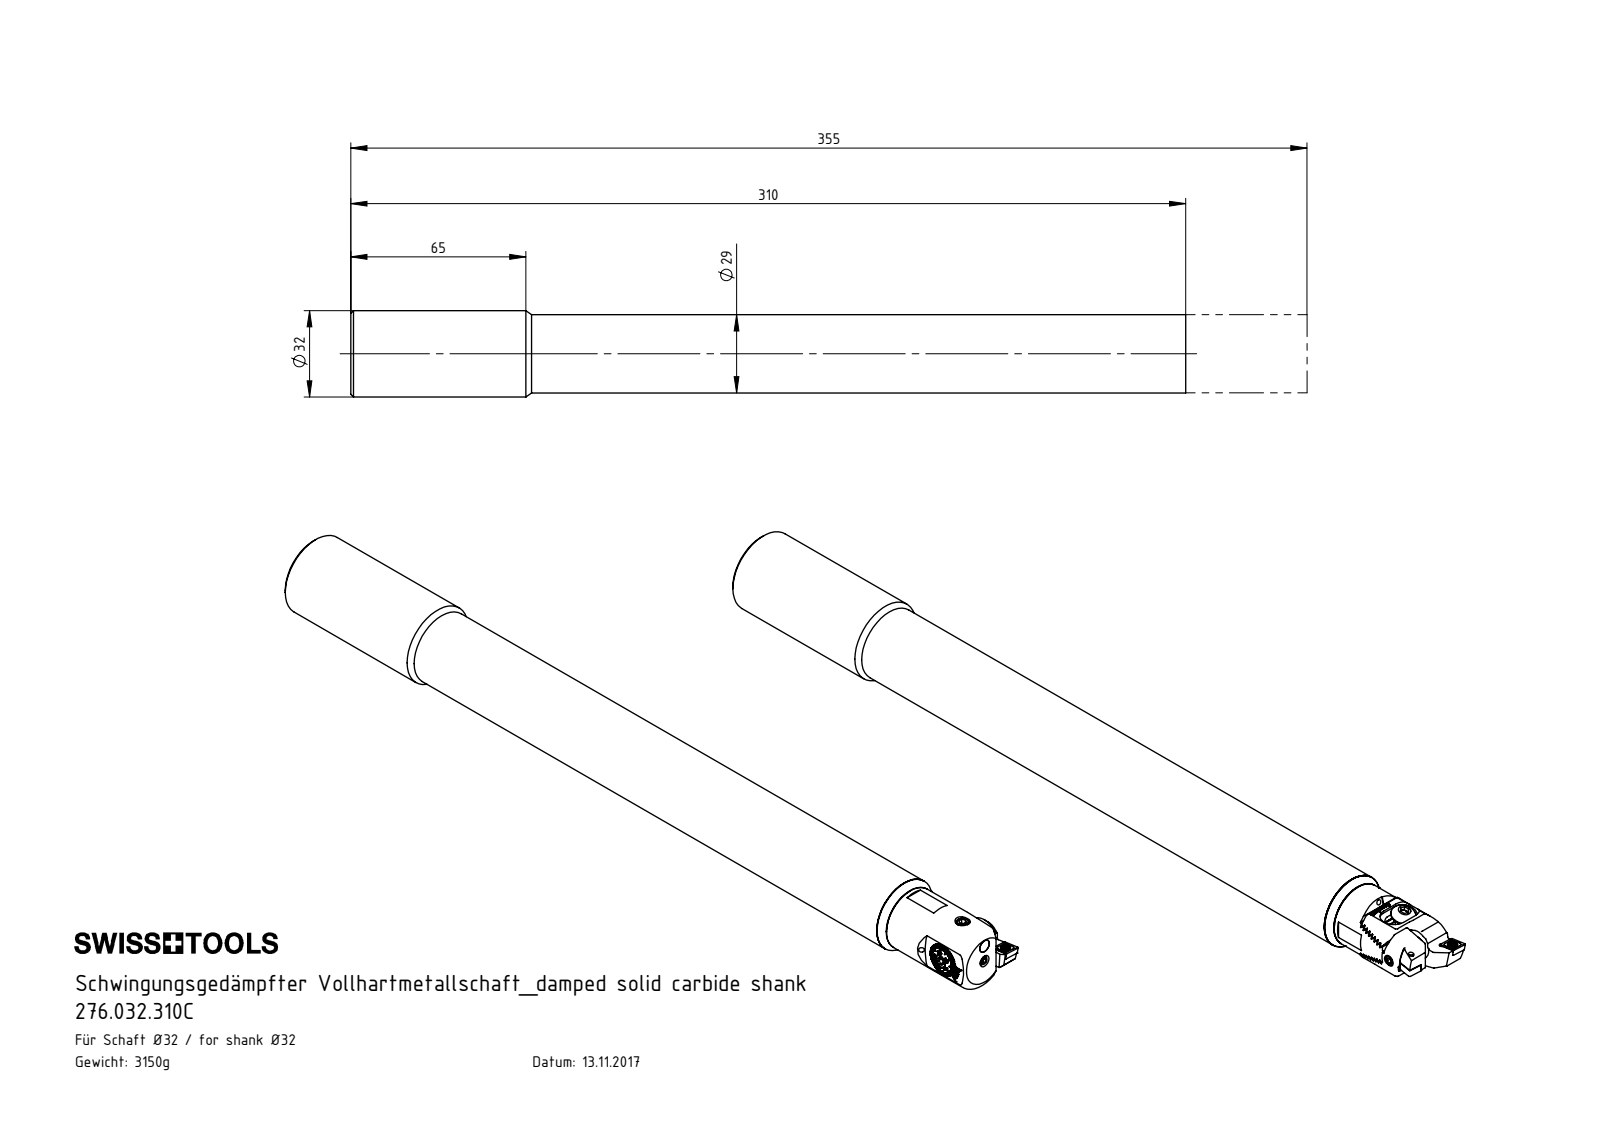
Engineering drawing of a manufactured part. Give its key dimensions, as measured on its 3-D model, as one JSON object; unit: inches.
{"part_name": "HP5-F25.031.045_A; U32-HP5.029.310_A; DIN 3771 - 11x1; HP5-ER1.019.036_A (+8 more)", "step_written_by": "SolidWorks 2017 (CONFIG_CONTROL_DESIGN)", "units": "inches", "bodies": {"solids": 23, "faces": 913, "planar": 387, "cylindrical": 178, "other": 348}, "overall_size": [13.976, 1.26, 1.26], "volume_in3": 14.14, "surface_area_in2": 88.27, "round_holes": [[0.079, 5], [0.165, 3], [0.081, 2], [0.083, 1], [0.094, 1], [0.106, 1], [0.11, 1], [0.118, 1], [0.13, 1], [0.152, 1], [0.197, 1], [0.217, 1]], "round_bosses_or_shafts": [[0.197, 2], [0.195, 2], [0.098, 2], [1.26, 1], [1.142, 1], [0.984, 1], [0.63, 1], [0.511, 1]], "partial_cylinders_radius": [[0.008, 6], [0.014, 5], [0.02, 4], [0.052, 2], [0.008, 1], [0.014, 1], [0.041, 1], [0.049, 1]], "face_to_face_distances": [12.205, 0.118, 10.787, 1.417, 12.323, 1.535, 0.315, 0.591, 13.864, 3.077], "hole_center_spacings": [0.151, 0.157, 0.176, 0.268, 0.372, 0.656]}
